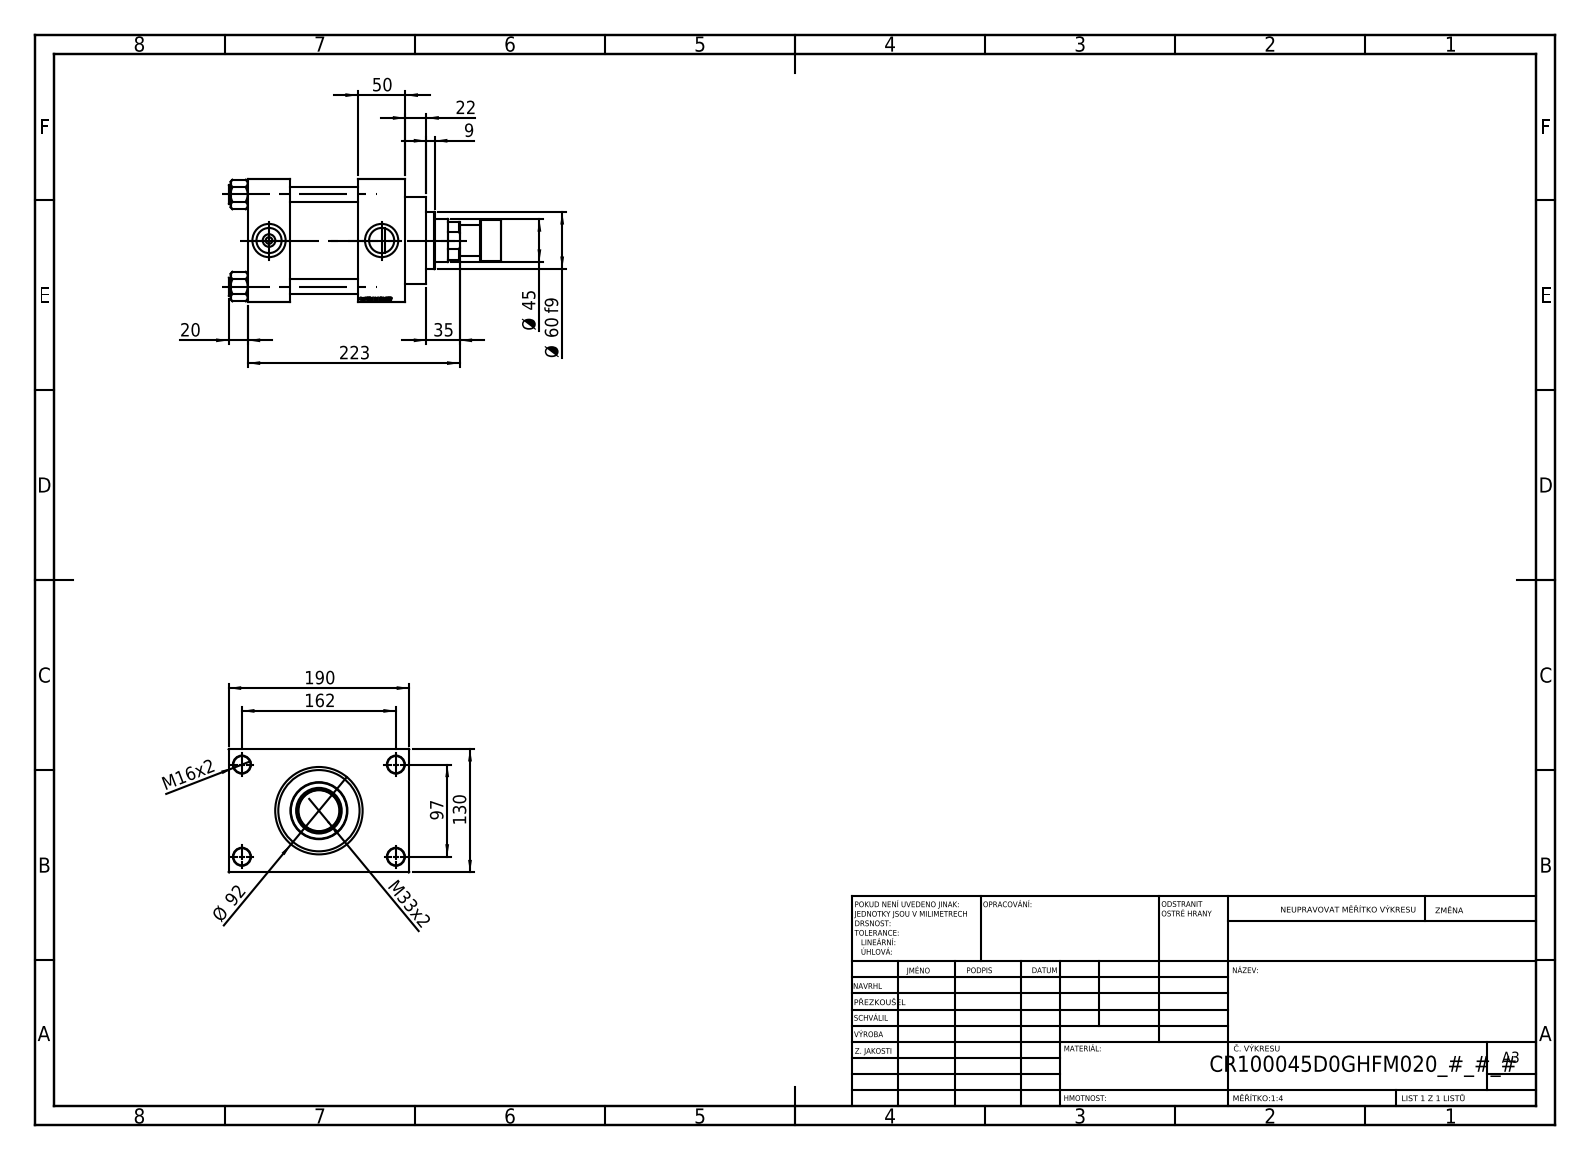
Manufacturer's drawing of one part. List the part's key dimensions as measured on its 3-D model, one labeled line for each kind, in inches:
Part name (STEP PRODUCT): V215CR_ROD_END_F; V215CR_D_Body; V215CR_VCP_D; NUT_M5_D (+2 more)
STEP written by: SolidWorks 2019 (CONFIG_CONTROL_DESIGN)
Units: inches
Bodies: 12 solids, 1164 faces (548 planar, 92 cylindrical, 524 other)
Overall size (bounding box): 11.299 × 7.48 × 5.118
Volume: 161.3 in³ · Surface area: 563 in²
Round holes (diameter × count): ⌀0.63 ×4, ⌀0.709 ×4, ⌀0.276 ×2, ⌀1.041 ×2, ⌀1.378 ×2, ⌀1.24 ×1, ⌀1.772 ×1, ⌀1.89 ×1, ⌀2.992 ×1, ⌀3.366 ×1, ⌀3.937 ×1
Round bosses / shafts (diameter × count): ⌀0.748 ×4, ⌀4.173 ×1, ⌀3.622 ×1, ⌀2.362 ×1, ⌀1.732 ×1, ⌀1.299 ×1
Main face-to-face distances: 5.118, 4.567, 1.772, 2.795, 6.535, 4.764, 1.969, 1.181, 6.299, 2.756
Hole centre spacings: 1.281, 2.698, 3.717, 3.815, 4.026, 5.096, 6.367, 3.819
